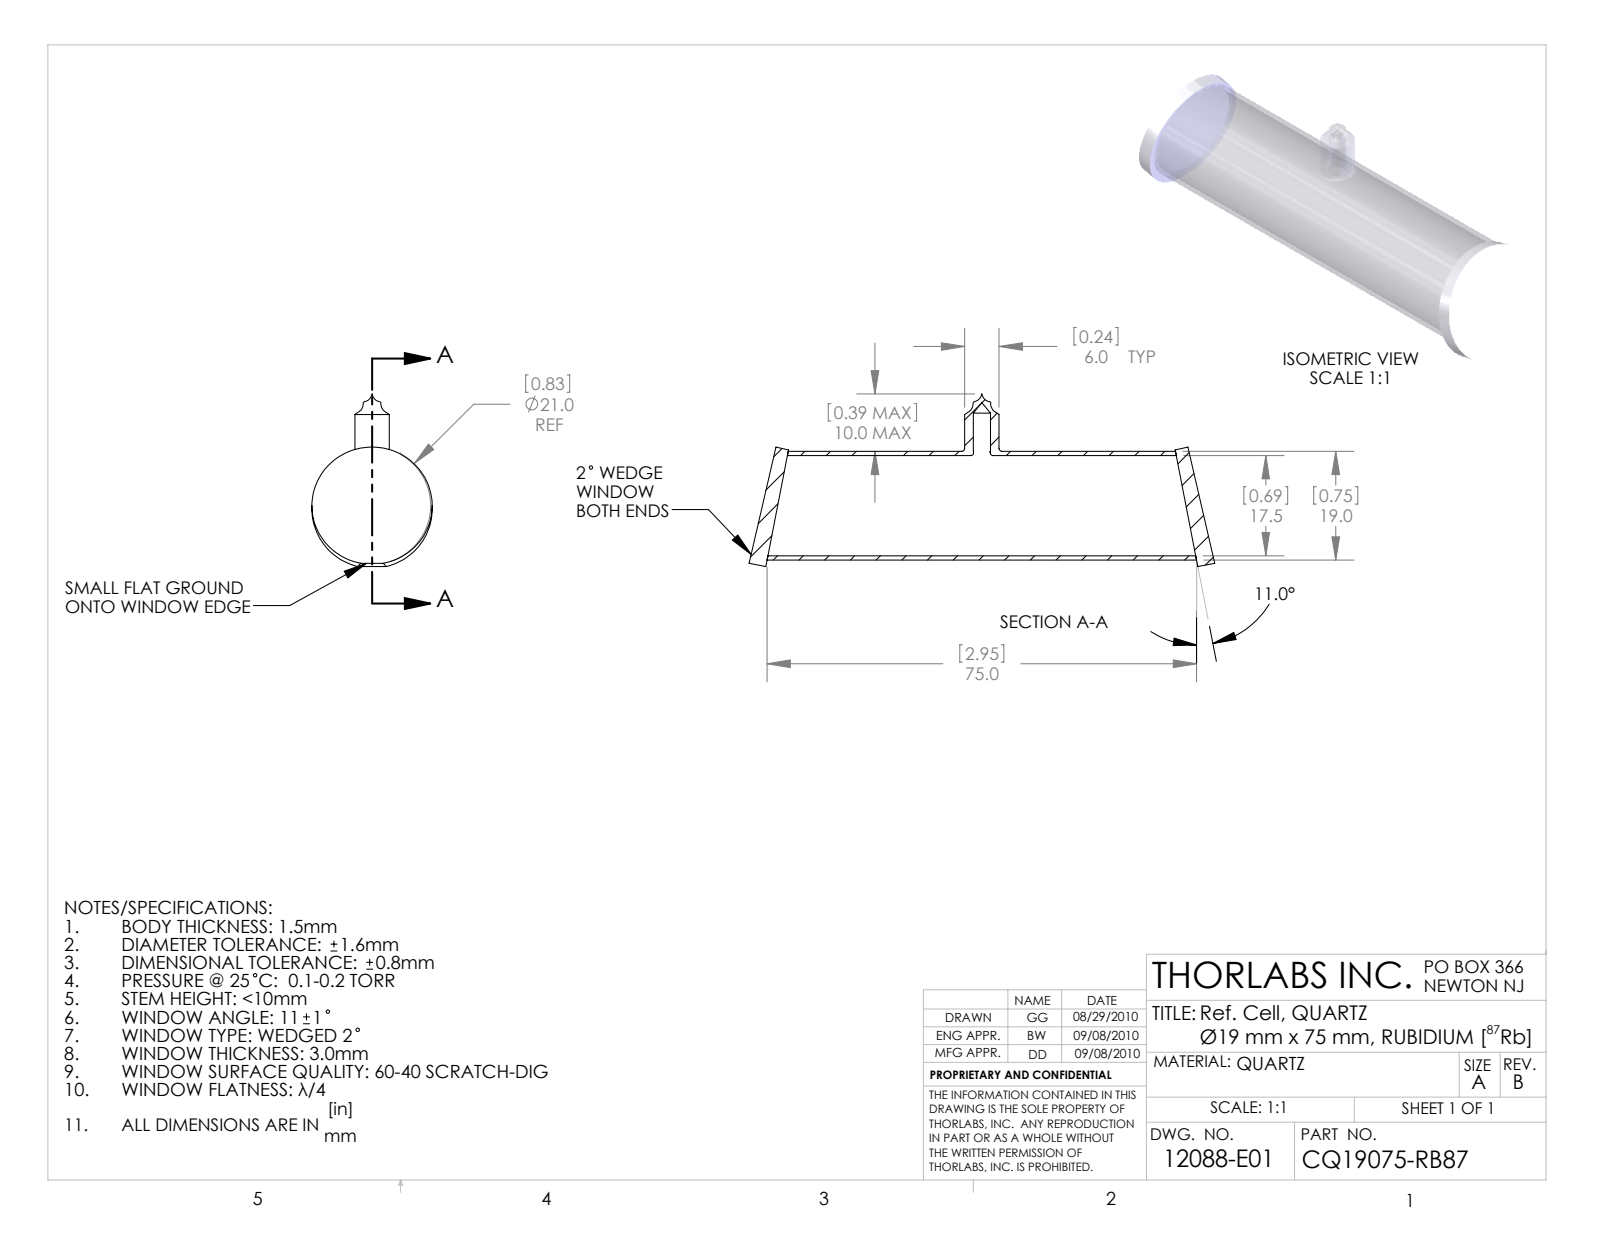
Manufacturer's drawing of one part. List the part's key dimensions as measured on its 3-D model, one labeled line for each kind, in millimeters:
Part name (STEP PRODUCT): 12088-E0W
STEP written by: SolidWorks 2009 (AUTOMOTIVE_DESIGN)
Units: millimetres
Bodies: 3 solids, 33 faces (8 planar, 17 cylindrical, 8 other)
Overall size (bounding box): 81.31 × 30.12 × 21
Volume: 5 042 mm³ · Surface area: 10 206 mm²
Round holes (diameter × count): ⌀2.91 ×1, ⌀3 ×1, ⌀17.5 ×1
Round bosses / shafts (diameter × count): ⌀21 ×2, ⌀19 ×1, ⌀6 ×1
